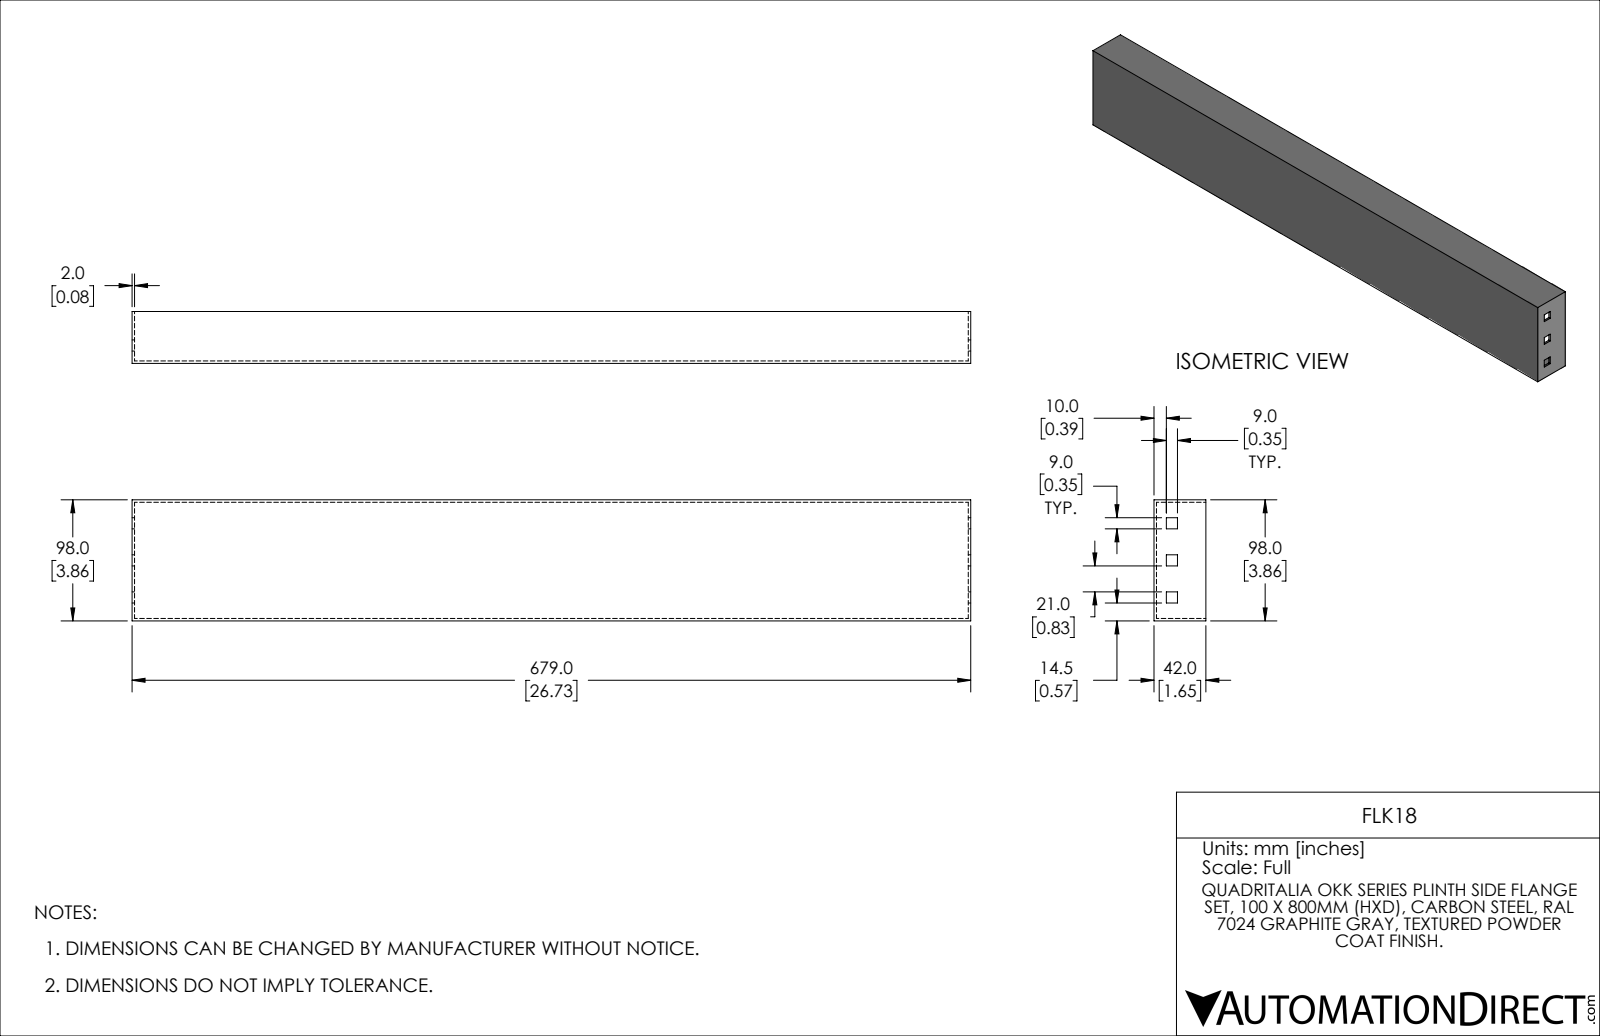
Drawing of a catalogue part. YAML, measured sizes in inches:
part_name: "FLK18"
step_written_by: "SolidWorks 2021 (CONFIG_CONTROL_DESIGN)"
units: inches
bodies: {solids: 1, faces: 35, planar: 35, cylindrical: 0, other: 0}
overall_size: [26.732, 3.858, 1.654]
volume: 15.61
surface_area: 402
face_to_face_distances: [0.079, 3.78, 3.858, 3.701, 26.654, 26.732, 26.575, 1.654, 1.575, 0.354]
